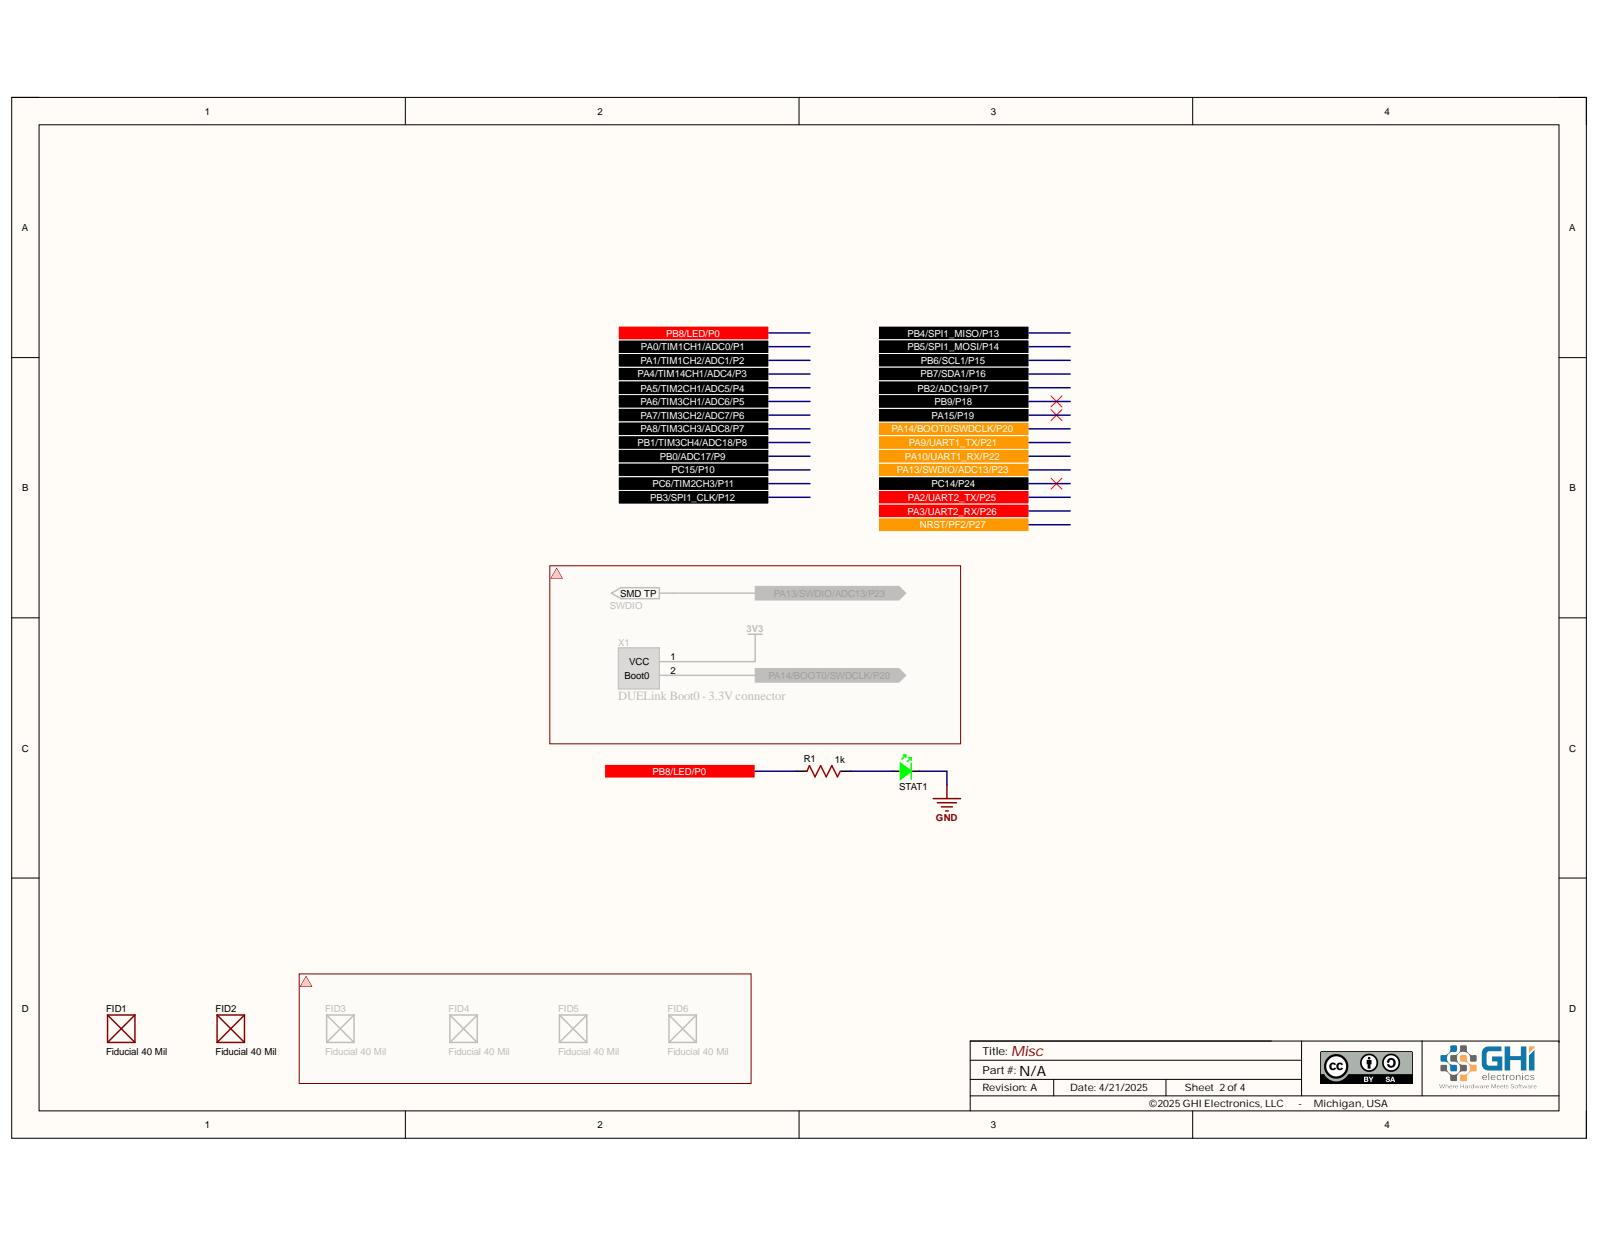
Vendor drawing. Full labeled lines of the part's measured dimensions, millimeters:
Part name (STEP PRODUCT): PCB; Board; J1; DUELink-U-Connector-BM04B-SRSS-TB (+7 more)
STEP written by: Open CASCADE 7.5 (AUTOMOTIVE_DESIGN)
Units: millimetres
Bodies: 79 solids, 1337 faces (983 planar, 254 cylindrical, 100 other)
Overall size (bounding box): 30.48 × 12.7 × 5.79
Volume: 591 mm³ · Surface area: 1 498 mm²
Round holes (diameter × count): ⌀0.9 ×24
Partial cylindrical surfaces — rounded edges, fillets, slot ends (radius × count): R0.12 ×35, R0.32 ×24, R0.15 ×14, R0.17 ×2, R0.18 ×2, R0.18 ×2
Main face-to-face distances: 1.36, 0.45, 0.53, 2.53, 26.62, 1, 2.28, 3.45, 0.37, 12.7
Hole centre spacings: 12.7, 10.16, 2.54, 5.08, 10.47, 7.62, 11.36, 14.37
